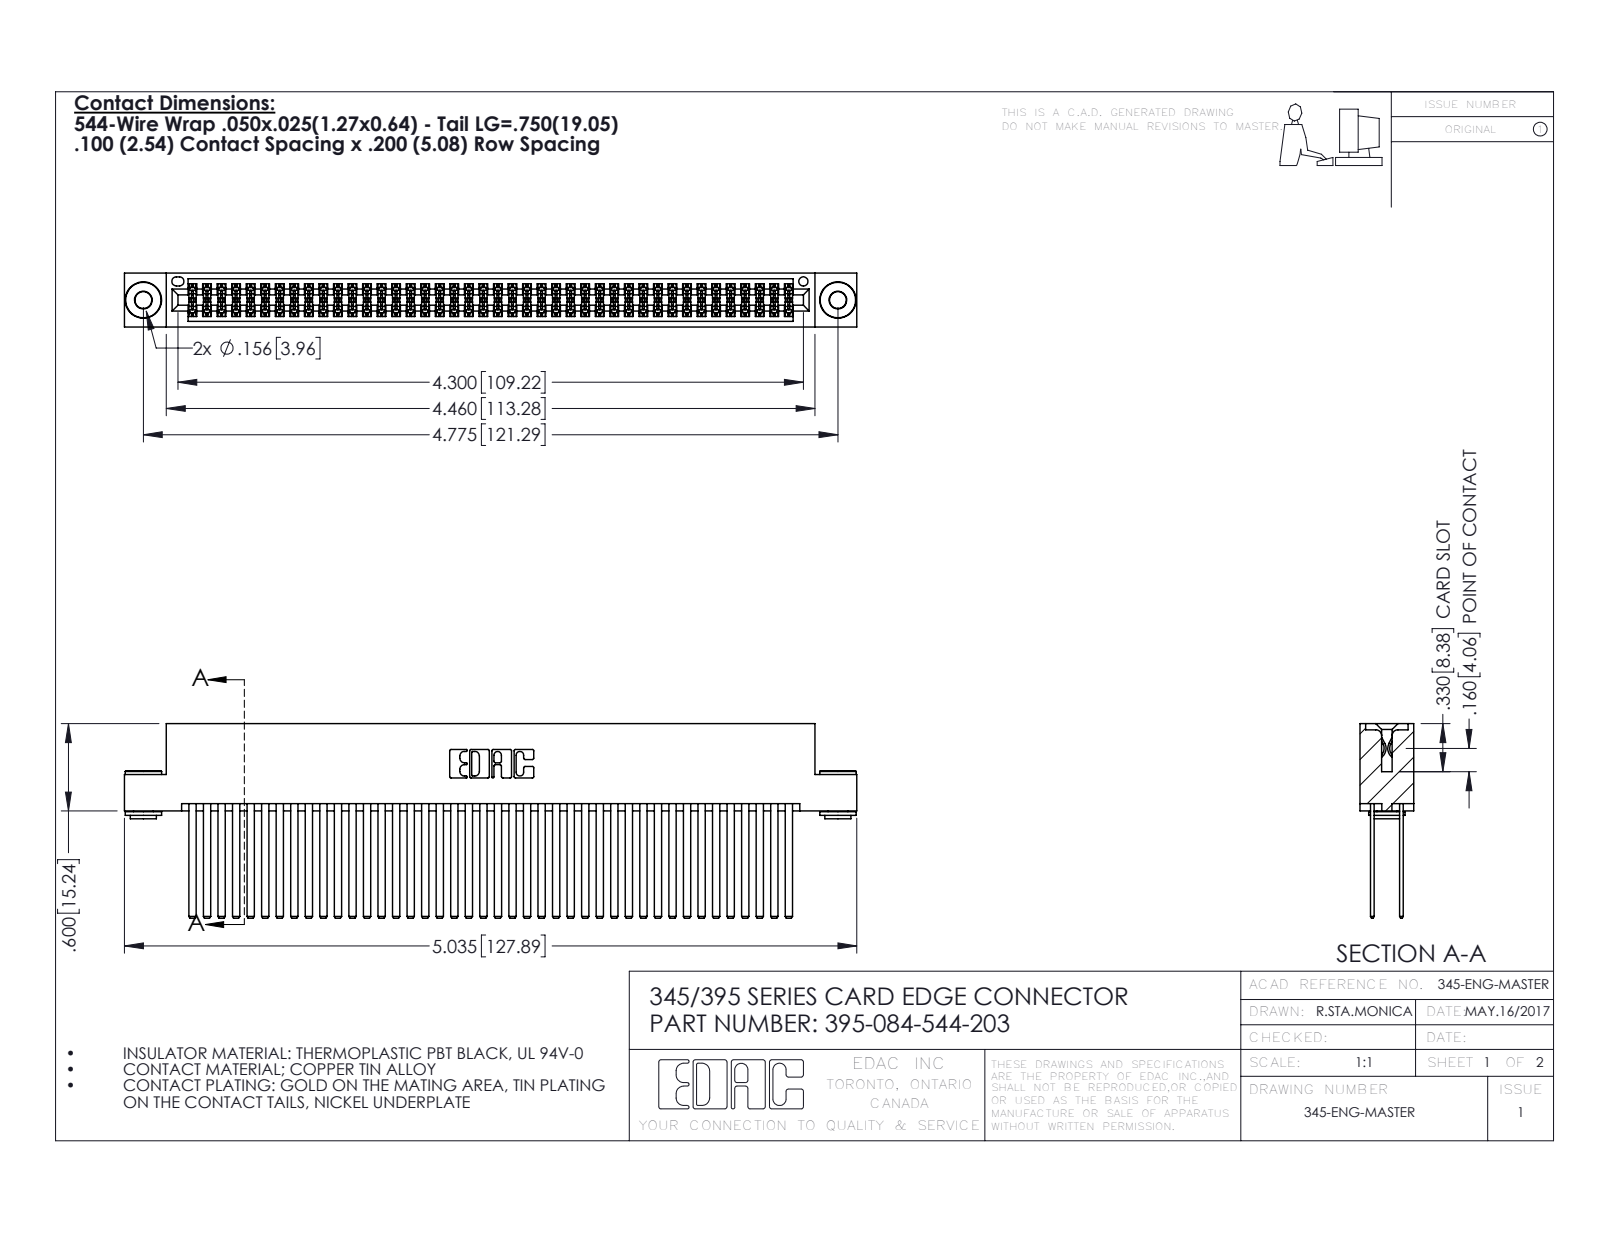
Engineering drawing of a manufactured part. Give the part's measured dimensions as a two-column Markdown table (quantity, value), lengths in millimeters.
| quantity | value |
| --- | --- |
| part name | 345-250-002_345-250-002-102; 345 Part_Flush Mounting Lugs - 0.156 Dia-TH; 395-084-544-203; 345-292-001_345-293-144 |
| STEP written by | SolidWorks 2016 (CONFIG_CONTROL_DESIGN) |
| units | millimeters |
| bodies | 87 solids, 3860 faces (2526 planar, 1326 cylindrical, 8 other) |
| overall size | 127.9 × 34 × 9.4 |
| volume | 13 600 mm³ |
| surface area | 23 790 mm² |
| round holes (diameter × count) | 2.9 × 2, 4 × 2, 1.6 × 1 |
| round bosses / shafts (diameter × count) | 6.4 × 2, 4.6 × 2, 3.5 × 2 |
| partial cylindrical surfaces (radius × count) | 0.2 × 126, 0.3 × 22, 0.2 × 6, 0.8 × 6, 0.7 × 3, 0.4 × 2, 0.5 × 2, 0.6 × 2 |
| main face-to-face distances | 5.1, 0.6, 1.8, 2.5, 6.9, 7.6, 5.7, 4.4, 9.4, 1.3 |
| hole center spacings | 6.9, 115.3, 121.3 |
